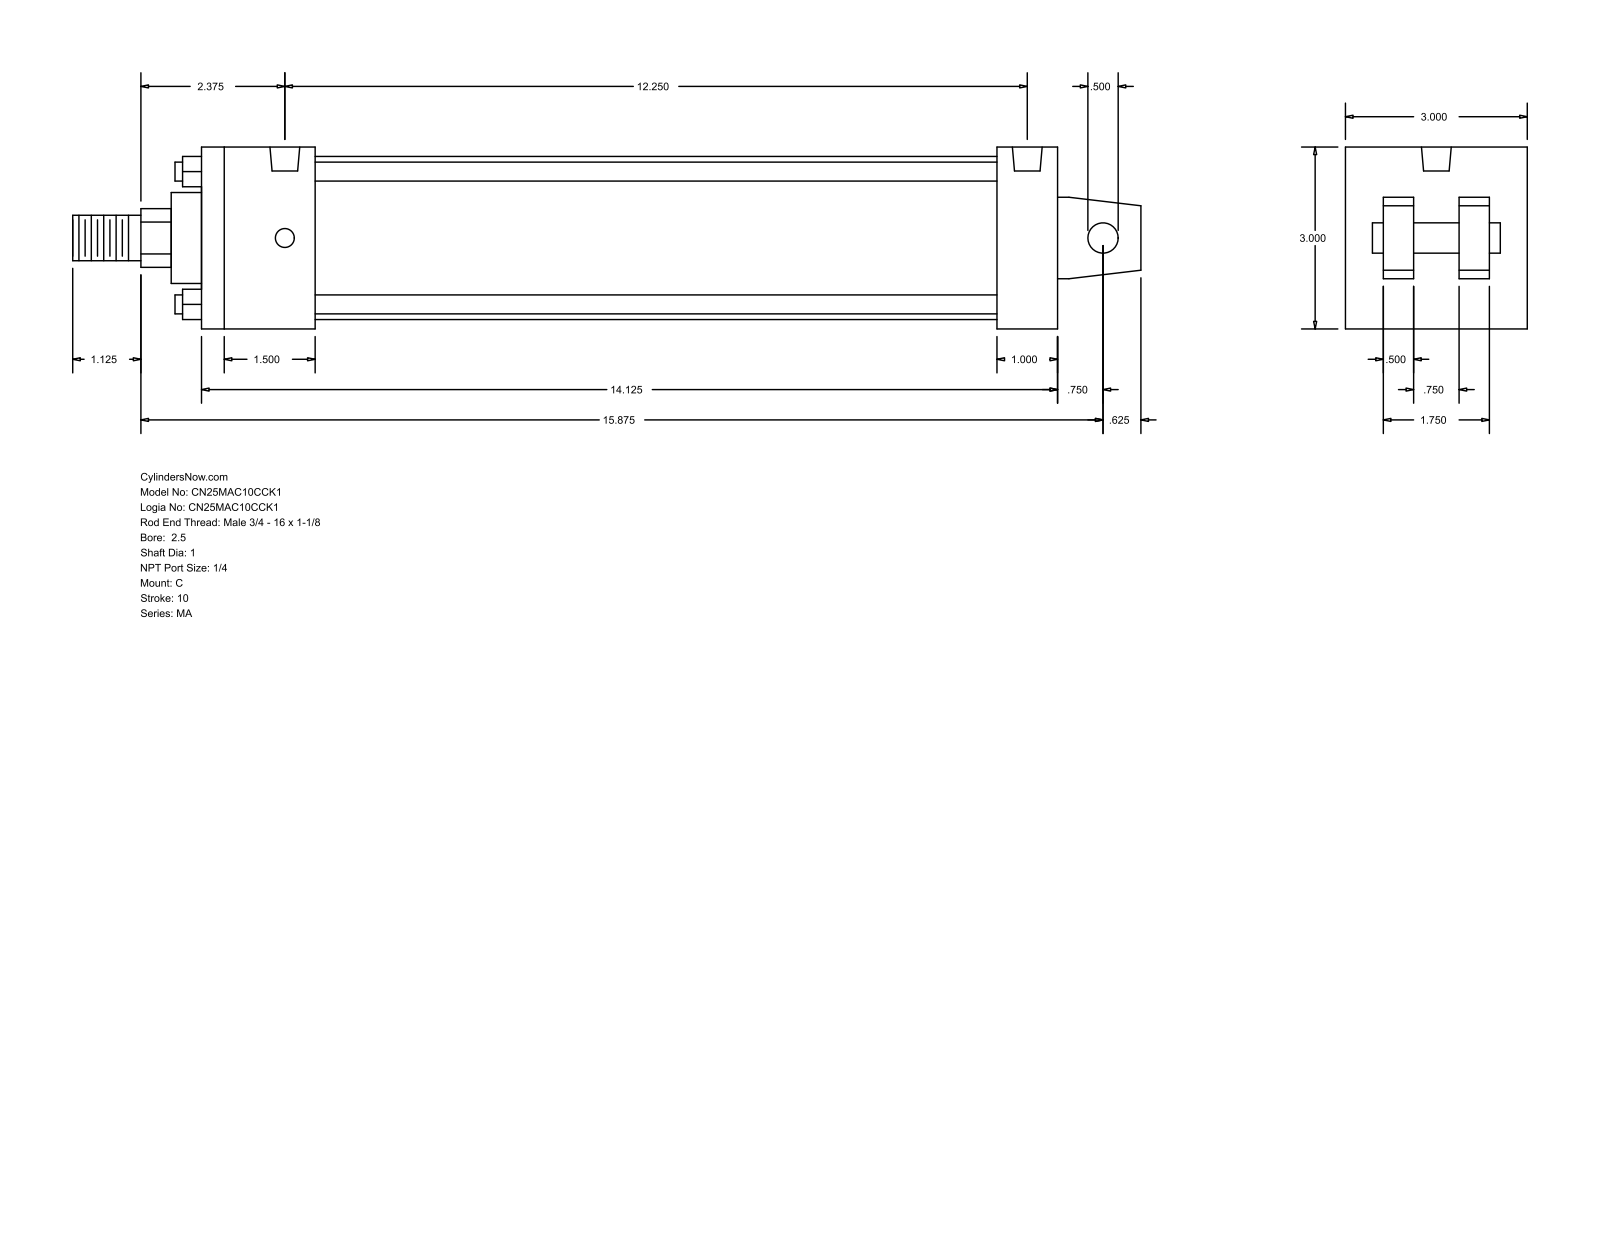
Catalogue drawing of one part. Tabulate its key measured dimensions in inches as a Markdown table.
| quantity | value |
| --- | --- |
| part name | MA_C__0250_1 |
| STEP written by | GSSL Pune (CONFIG_CONTROL_DESIGN) |
| units | inches |
| bodies | 0 solids, 103 faces (76 planar, 27 cylindrical, 0 other) |
| overall size | 17.625 × 3 × 3 |
| round holes (diameter × count) | 0.313 × 4, 0.492 × 2 |
| round bosses / shafts (diameter × count) | 0.313 × 4, 2.69 × 1, 1.5 × 1, 1 × 1, 0.75 × 1, 0.5 × 1 |
| partial cylindrical surfaces (radius × count) | 0.484 × 1 |
| main face-to-face distances | 3, 1.875, 14.125, 0.5, 2.375, 0.625, 1.125, 13.125, 11.25, 12.25 |
| hole center spacings | 12.25 |
